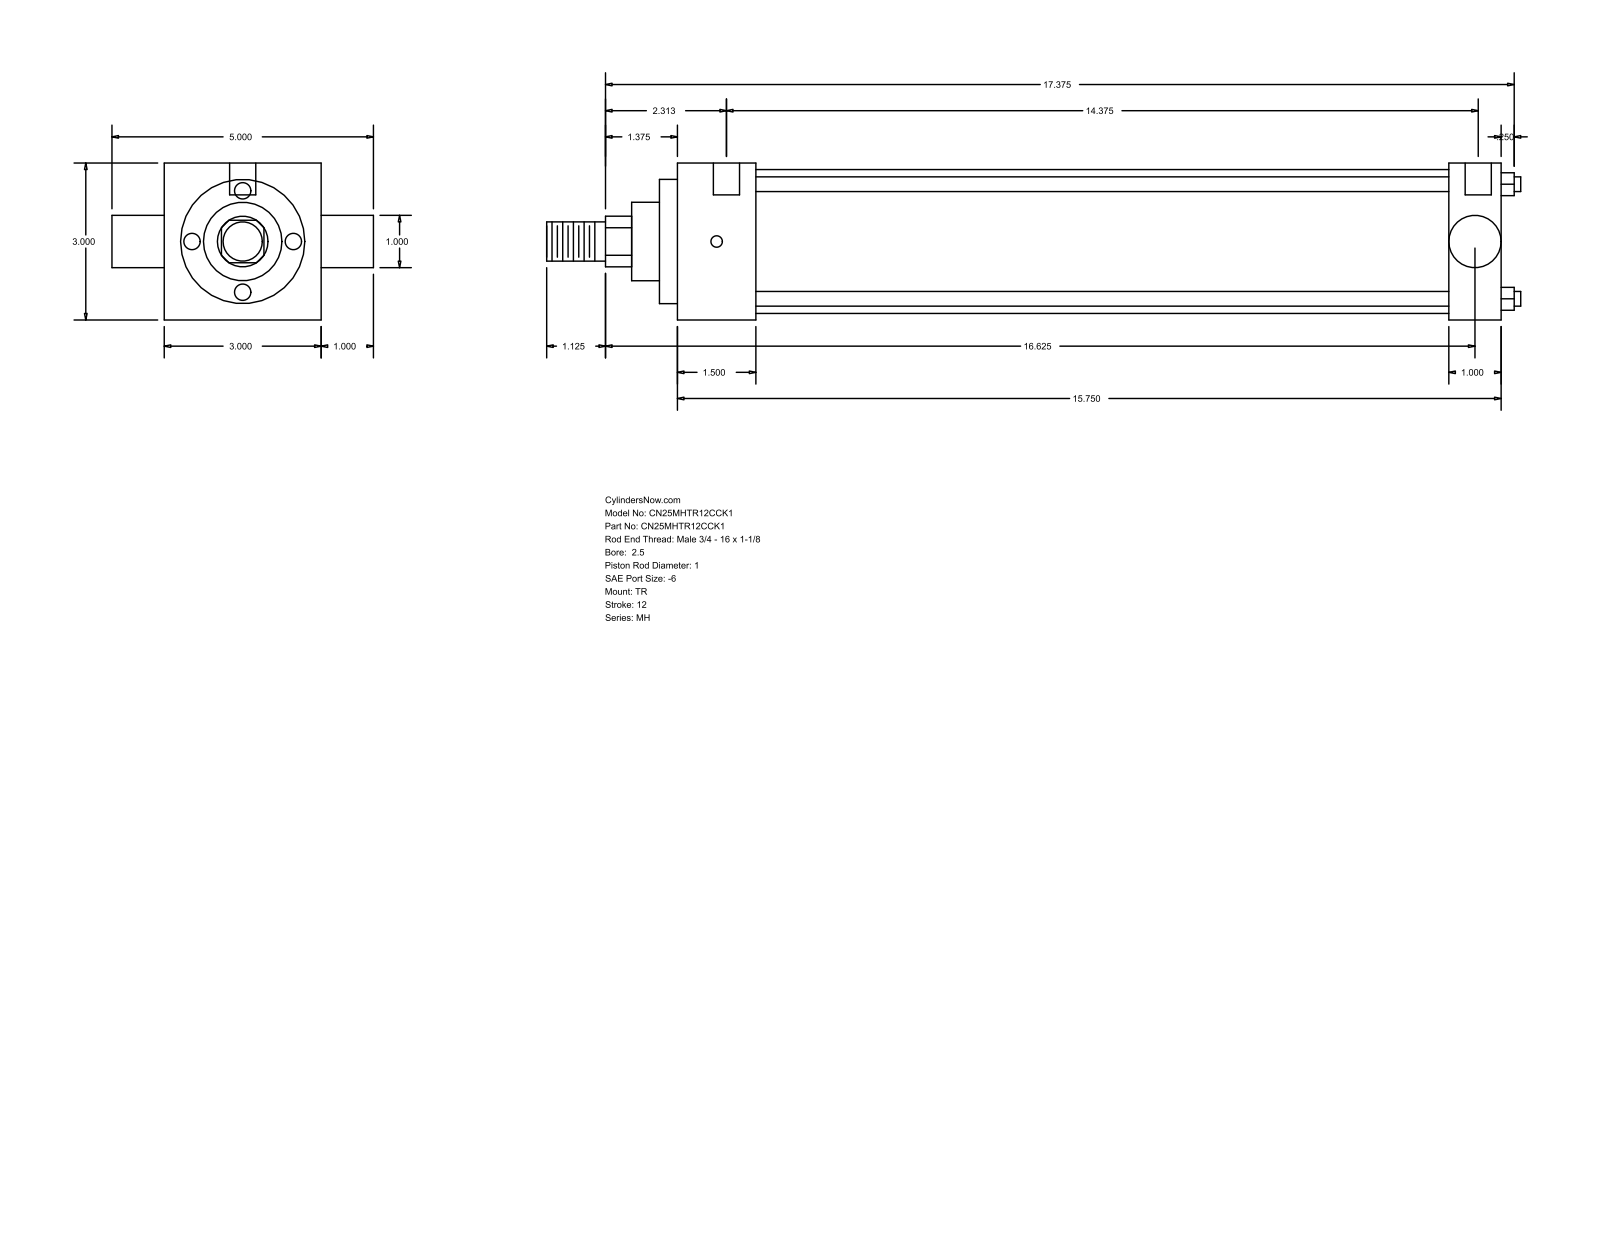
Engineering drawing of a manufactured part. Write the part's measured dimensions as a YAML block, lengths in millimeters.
part_name: "MH_TR__0250_1"
step_written_by: "GSSL Pune (CONFIG_CONTROL_DESIGN)"
units: millimeters
bodies: {solids: 0, faces: 86, planar: 61, cylindrical: 25, other: 0}
overall_size: [473.07, 127, 76.2]
round_holes:
  - {diameter: 5.56, count: 3}
  - {diameter: 12.7, count: 2}
round_bosses_or_shafts:
  - {diameter: 7.14, count: 4}
  - {diameter: 69.85, count: 1}
  - {diameter: 60.33, count: 1}
  - {diameter: 38.1, count: 1}
  - {diameter: 25.4, count: 1}
  - {diameter: 25.35, count: 1}
  - {diameter: 19.05, count: 1}
partial_cylinders:
  - {radius: 12.29, count: 1}
face_to_face_distances: [76.2, 400.06, 38.11, 361.95, 374.65, 336.54, 25.41, 8.73, 46.84, 383.38]
hole_center_spacings: [3.18, 4.76, 365.12, 368.3, 369.88, 373.06]
